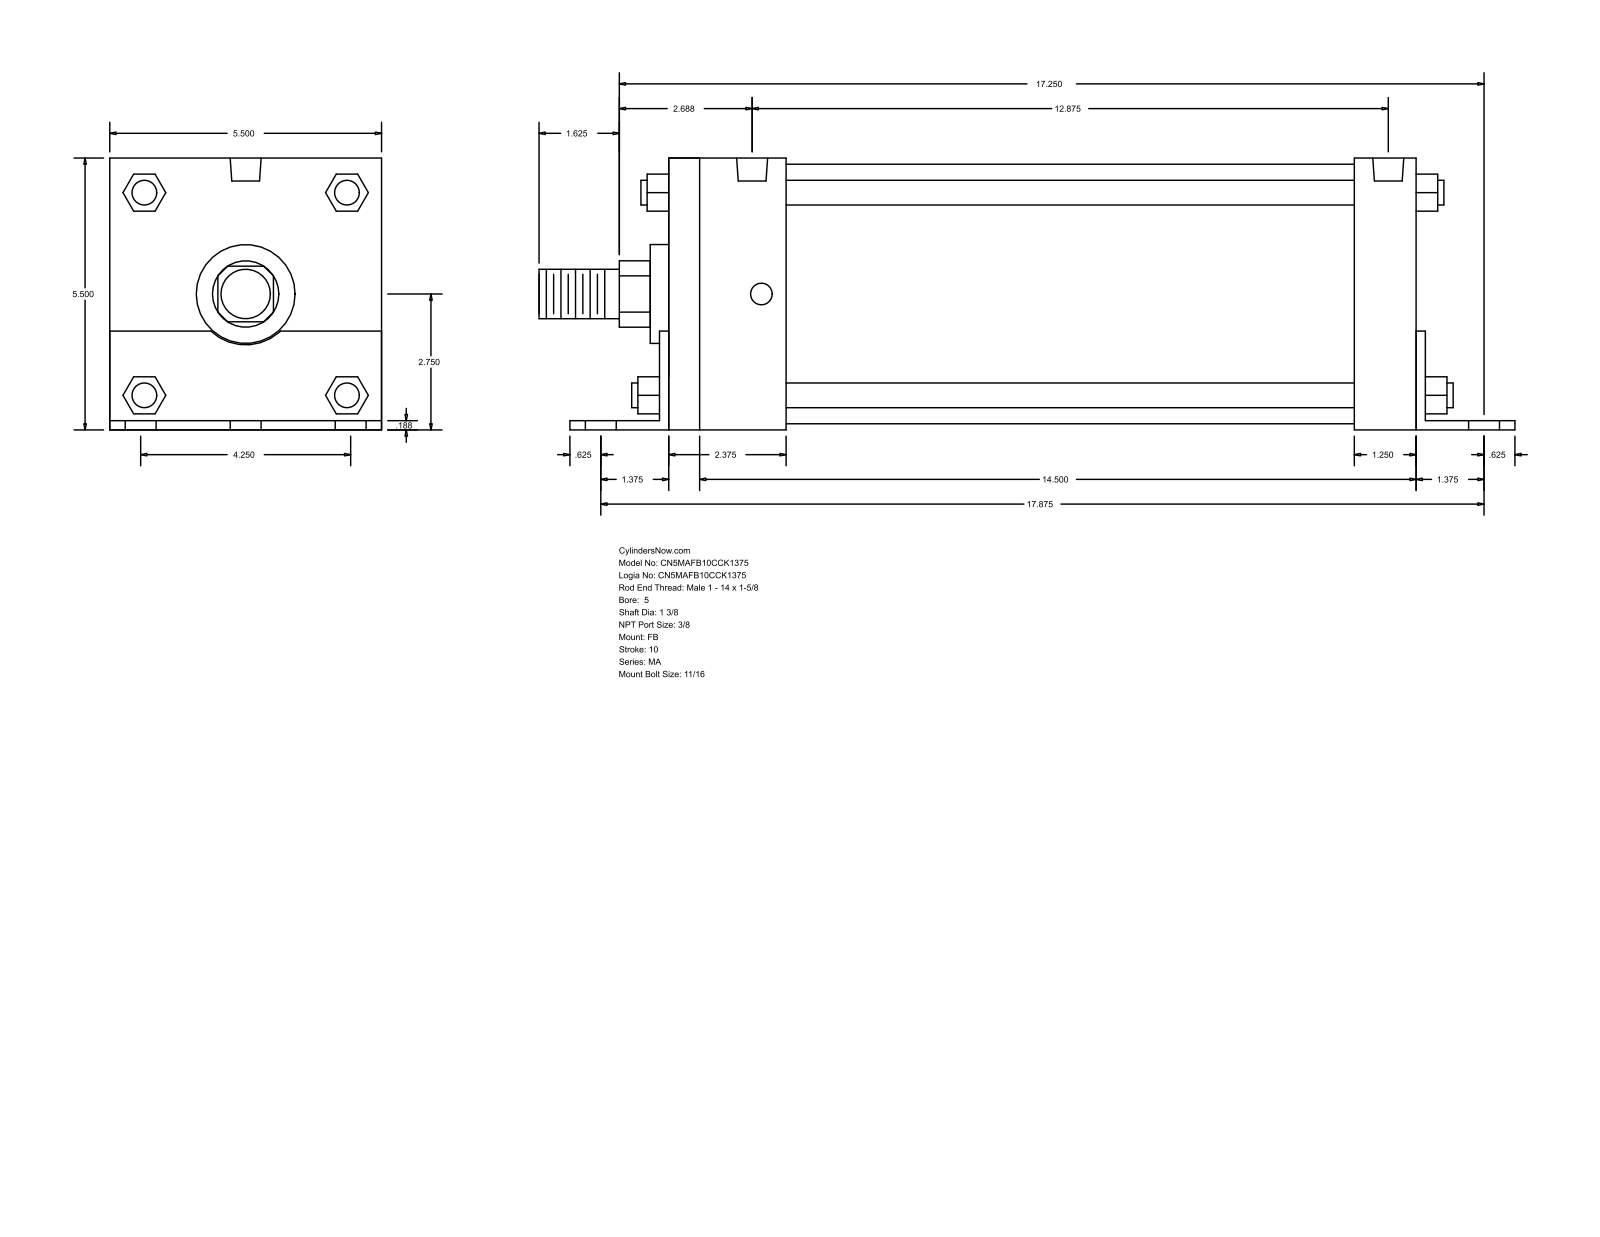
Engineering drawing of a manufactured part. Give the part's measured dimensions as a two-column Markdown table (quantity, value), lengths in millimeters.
| quantity | value |
| --- | --- |
| part name | MA_FB__0500_1.375 |
| STEP written by | GSSL Pune (CONFIG_CONTROL_DESIGN) |
| units | millimeters |
| bodies | 0 solids, 140 faces (105 planar, 35 cylindrical, 0 other) |
| overall size | 501.65 × 139.75 × 139.7 |
| round holes (diameter × count) | 17.46 × 6, 11.11 × 4, 15.93 × 2 |
| round bosses / shafts (diameter × count) | 12.7 × 4, 133.35 × 1, 50.8 × 1, 34.92 × 1, 25.4 × 1 |
| partial cylindrical surfaces (radius × count) | 17.06 × 1, 26.16 × 1 |
| main face-to-face distances | 139.7, 4.76, 139.75, 4.71, 134.99, 384.17, 4.77, 388.94, 388.93, 393.7 |
| hole center spacings | 53.98, 457.23, 454.03, 4.77, 73.04, 76.34, 94.68, 98.64 |
